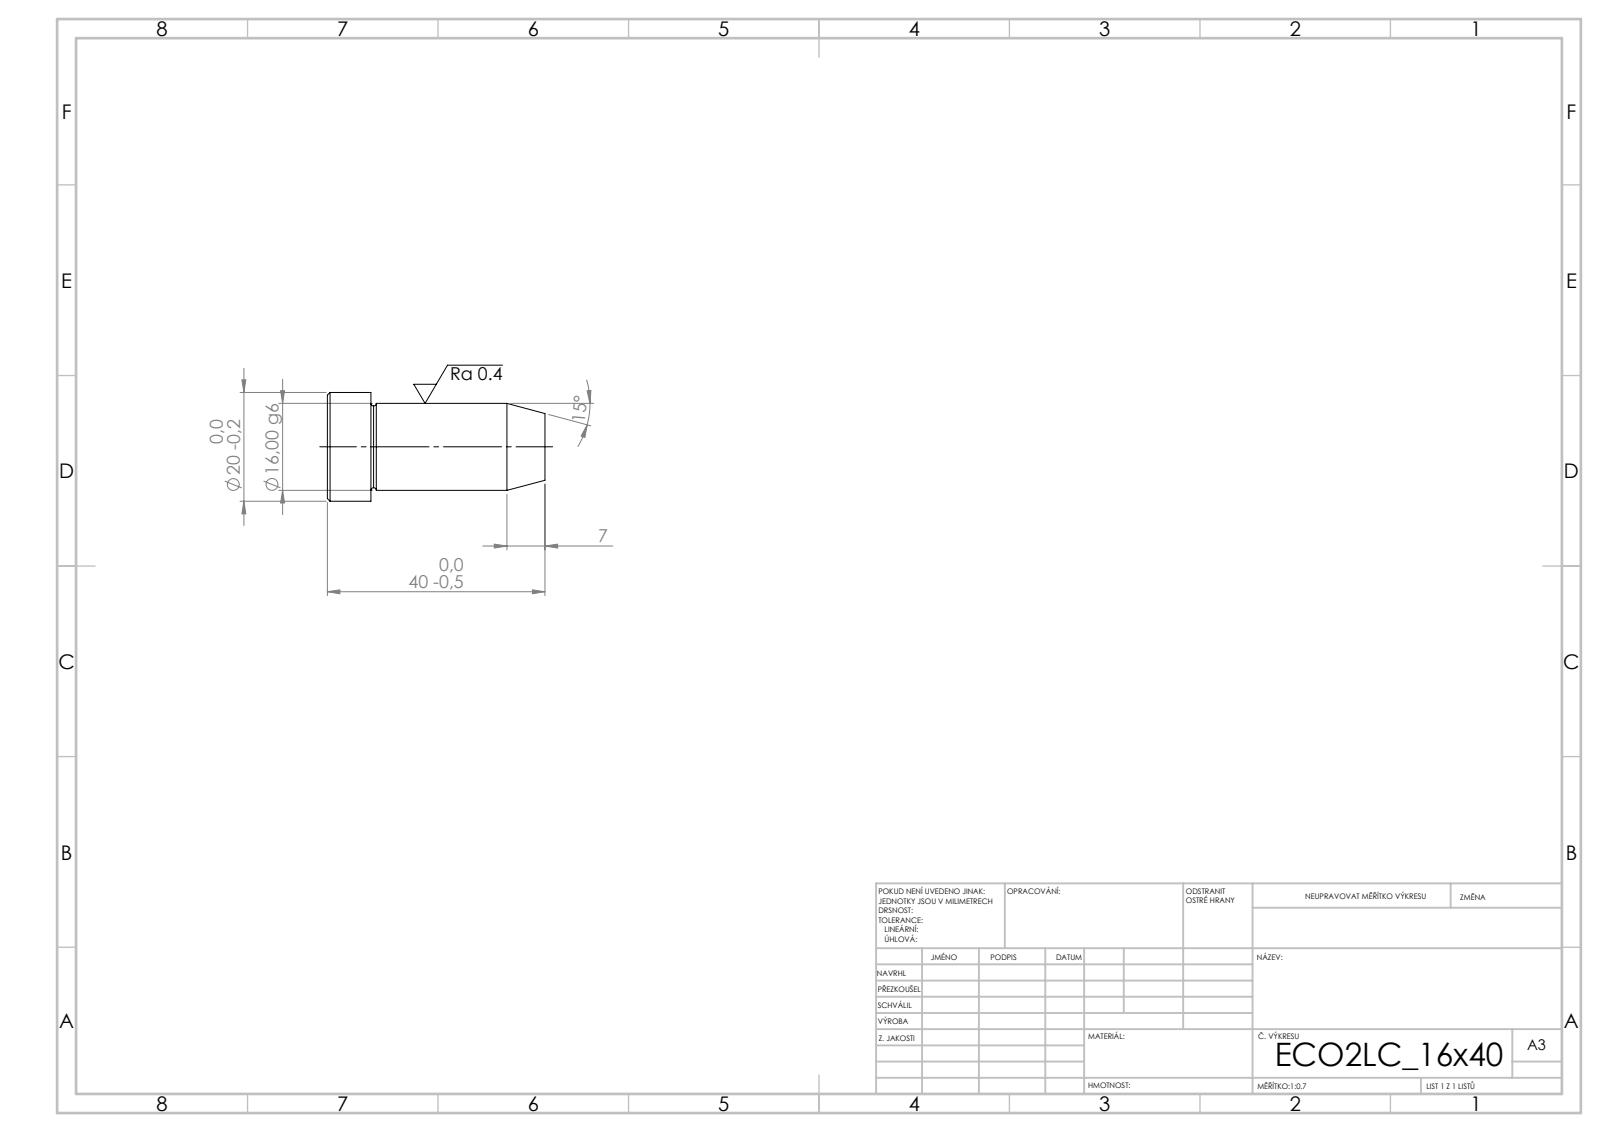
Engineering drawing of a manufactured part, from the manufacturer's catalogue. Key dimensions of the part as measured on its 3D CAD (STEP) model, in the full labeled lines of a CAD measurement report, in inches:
STEP written by: SolidWorks 2019 (CONFIG_CONTROL_DESIGN)
Units: inches
Bodies: 1 solid, 15 faces (3 planar, 4 cylindrical, 8 other)
Overall size (bounding box): 1.575 × 0.787 × 0.787
Volume: 0.526 in³ · Surface area: 4.081 in²
Round bosses / shafts (diameter × count): ⌀0.787 ×1, ⌀0.63 ×1
Main face-to-face distances: 1.575, 1.26, 0.315
